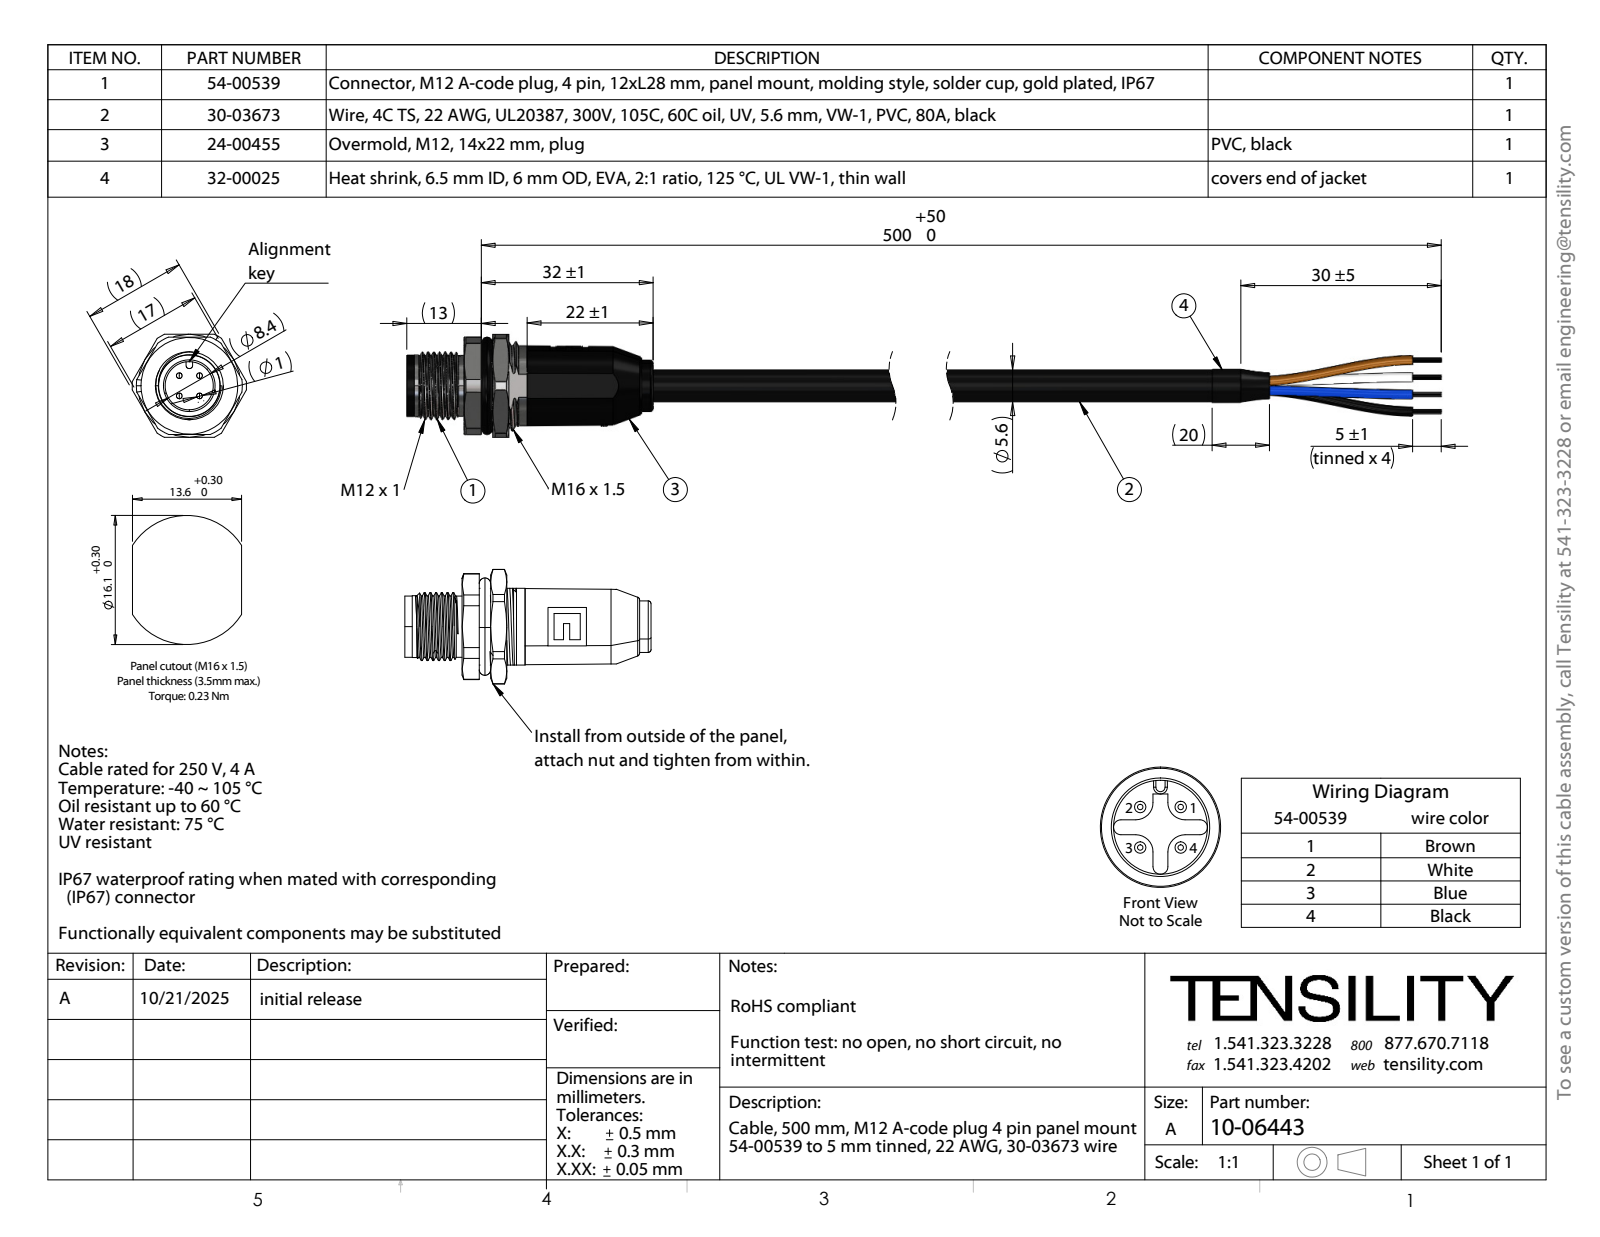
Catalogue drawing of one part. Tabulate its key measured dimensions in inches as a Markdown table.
| quantity | value |
| --- | --- |
| part name | 54-00539; 56-00046; 30-03673_spec; 24-00455 (+2 more) |
| STEP written by | SolidWorks 2025 (CONFIG_CONTROL_DESIGN) |
| units | inches |
| bodies | 150 solids, 1215 faces (474 planar, 576 cylindrical, 165 other) |
| overall size | 8.976 × 0.787 × 0.709 |
| volume | 0.582 in³ |
| surface area | 52.91 in² |
| round holes (diameter × count) | 0.063 × 4, 0.039 × 3, 0.038 × 1, 0.153 × 1, 0.169 × 1, 0.256 × 1, 0.331 × 1, 0.37 × 1, 0.378 × 1, 0.48 × 1, 0.579 × 1 |
| round bosses / shafts (diameter × count) | 0.059 × 4, 0.055 × 4, 0.549 × 1, 0.492 × 1, 0.467 × 1, 0.433 × 1, 0.425 × 1, 0.421 × 1 |
| partial cylindrical surfaces (radius × count) | 0.02 × 2, 0.277 × 1, 0.311 × 1, 0.364 × 1, 0.394 × 1 |
| main face-to-face distances | 0.315, 0.433, 0.079, 0.02, 0.059, 0.118, 0.689, 0.709, 0.394, 0.11 |
| hole center spacings | 0.019, 0.015, 0.064, 0.012, 0.013, 0.07, 0.013, 0.057 |
